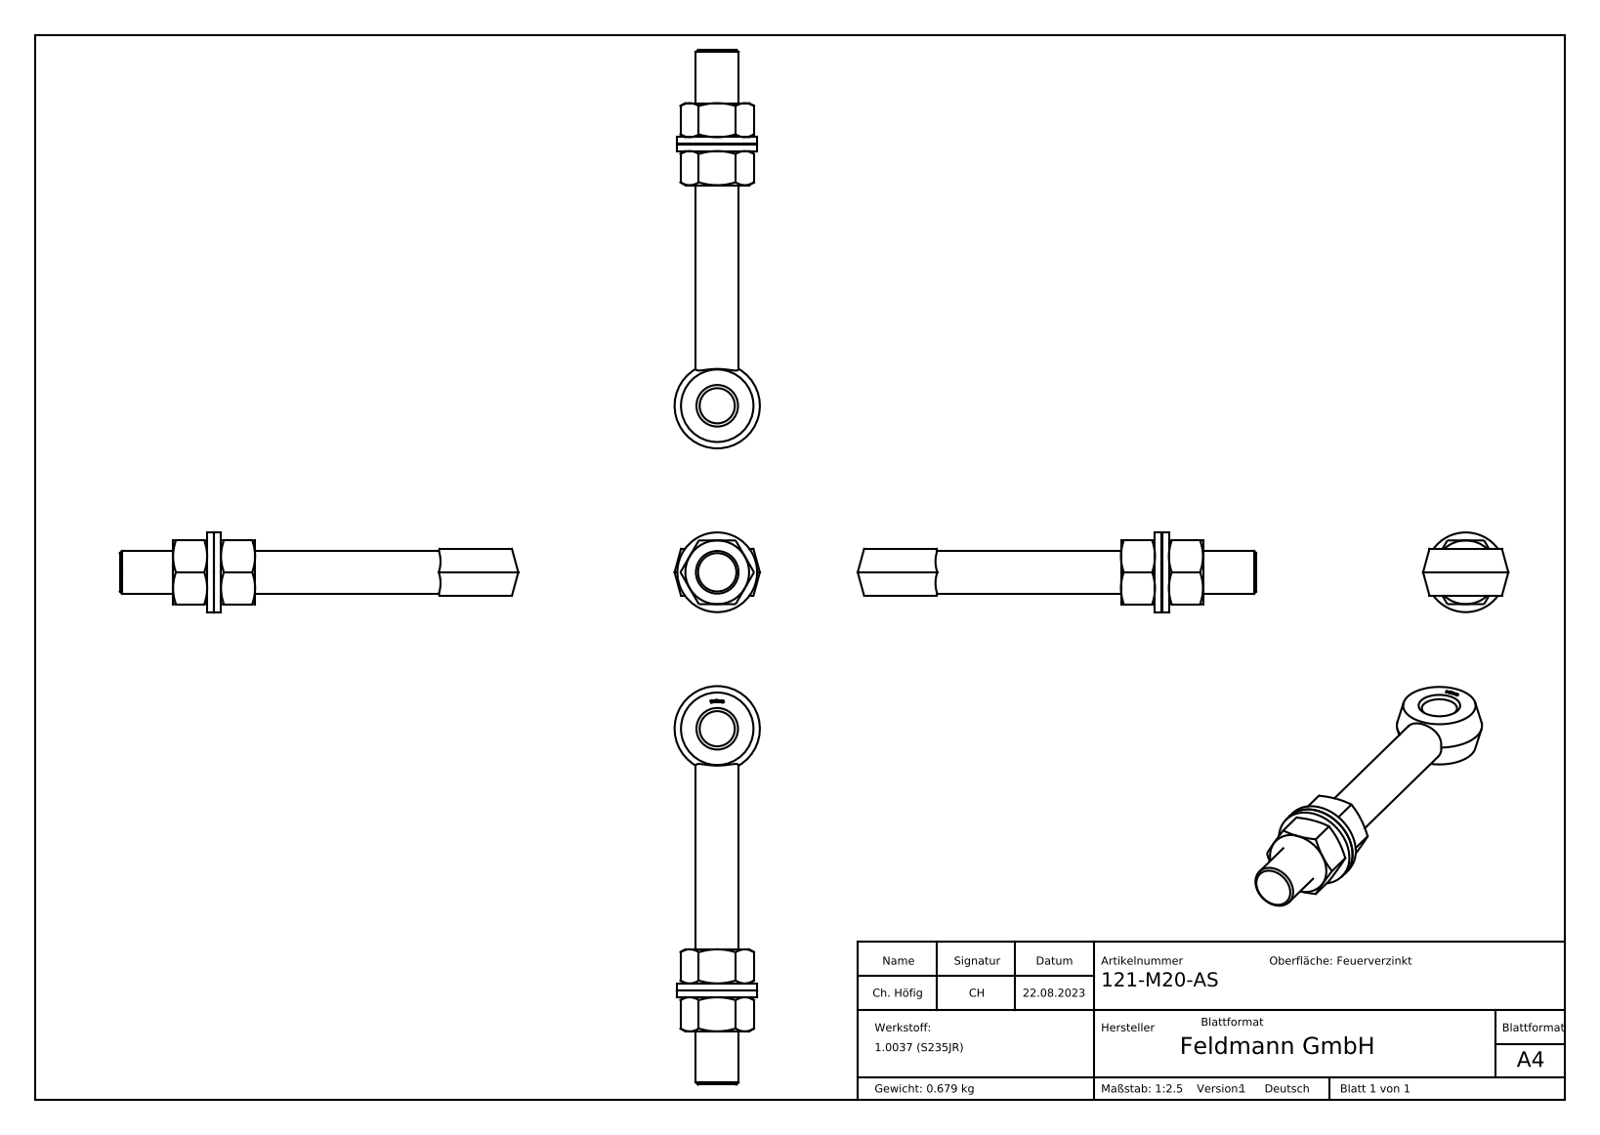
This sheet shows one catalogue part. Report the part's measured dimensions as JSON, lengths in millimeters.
{"part_name": "121-Mxx-AS Teil2_121-M20-AS Teil2; 121-Mxx-AS Teil1_121-M20-AS Teil1; 121-Mxx-AS Teil3_121-M20-AS Teil3; 121-M20-AS", "step_written_by": "SolidWorks 2018 (CONFIG_CONTROL_DESIGN)", "units": "millimeters", "bodies": {"solids": 5, "faces": 170, "planar": 93, "cylindrical": 8, "other": 69}, "overall_size": [187, 40, 37.4], "volume_mm3": 87097, "surface_area_mm2": 25500, "round_holes": [[16.5, 1], [17.5, 1], [21.8, 1]], "round_bosses_or_shafts": [[37.4, 1], [20, 1]], "face_to_face_distances": [29.9, 3.2, 3.3, 6.5, 3.95, 25.95, 16, 19.2, 19.3, 22.5]}
